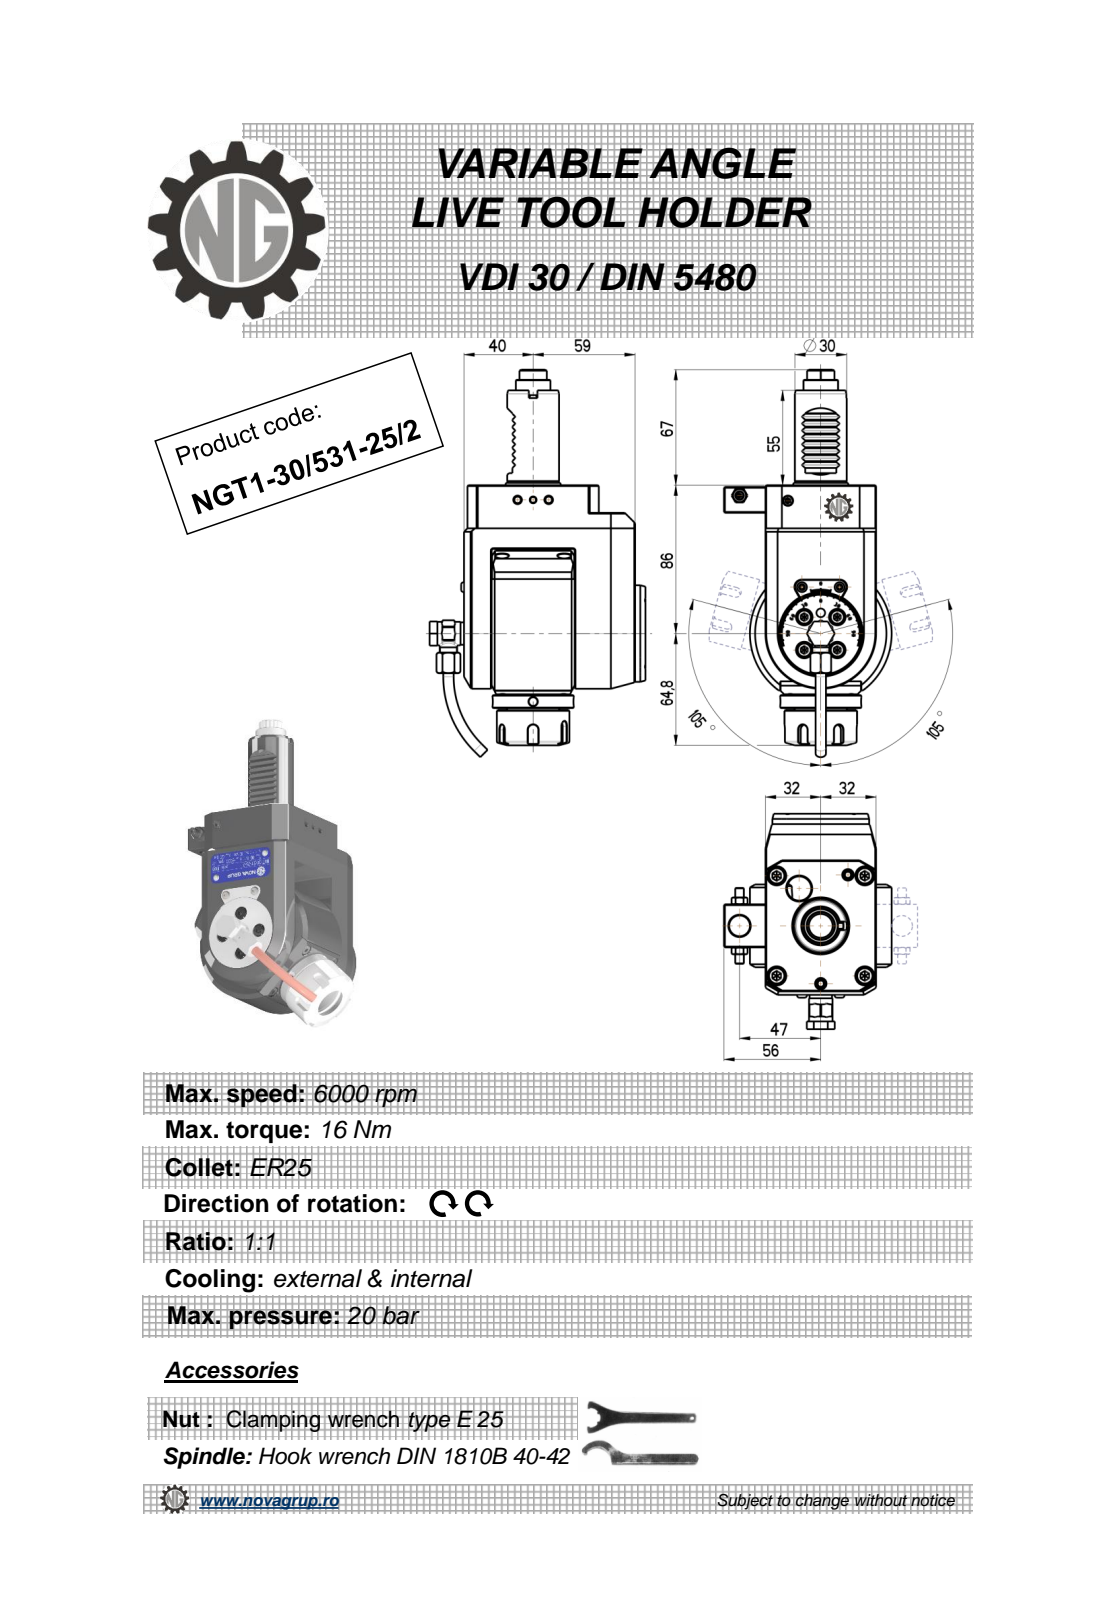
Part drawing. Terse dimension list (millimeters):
name: NGT1_30_531_25_2
written by: PRO/ENGINEER BY PARAMETRIC TECHNOLOGY CORPORATION, 2010280 (CONFIG_CONTROL_DESIGN)
unit: mm
bodies: 1 solid, 647 faces (239 planar, 213 cylindrical, 195 other)
size: 224.67 × 124.9 × 97
volume: 802 011 mm³; area: 75 476 mm²
holes: 5× ⌀4, 1× ⌀3, 1× ⌀4.2, 1× ⌀6.2, 1× ⌀9, 1× ⌀9.5, 1× ⌀11, 1× ⌀12, 1× ⌀20.3
bosses: 2× ⌀10, 2× ⌀6, 2× ⌀5.7, 1× ⌀56, 1× ⌀42, 1× ⌀40, 1× ⌀32.99, 1× ⌀30
rounds: 36× R1.98, 12× R0.26, 8× R0.3, 6× R0.16, 5× R3, 4× R0.5, 2× R1, 1× R7.29
face distances: 64, 16, 37, 6, 99, 105, 21, 14, 62, 83
hole spacings: 0.4, 38.95, 47, 49, 49.4, 67.9, 68.19, 92.78
